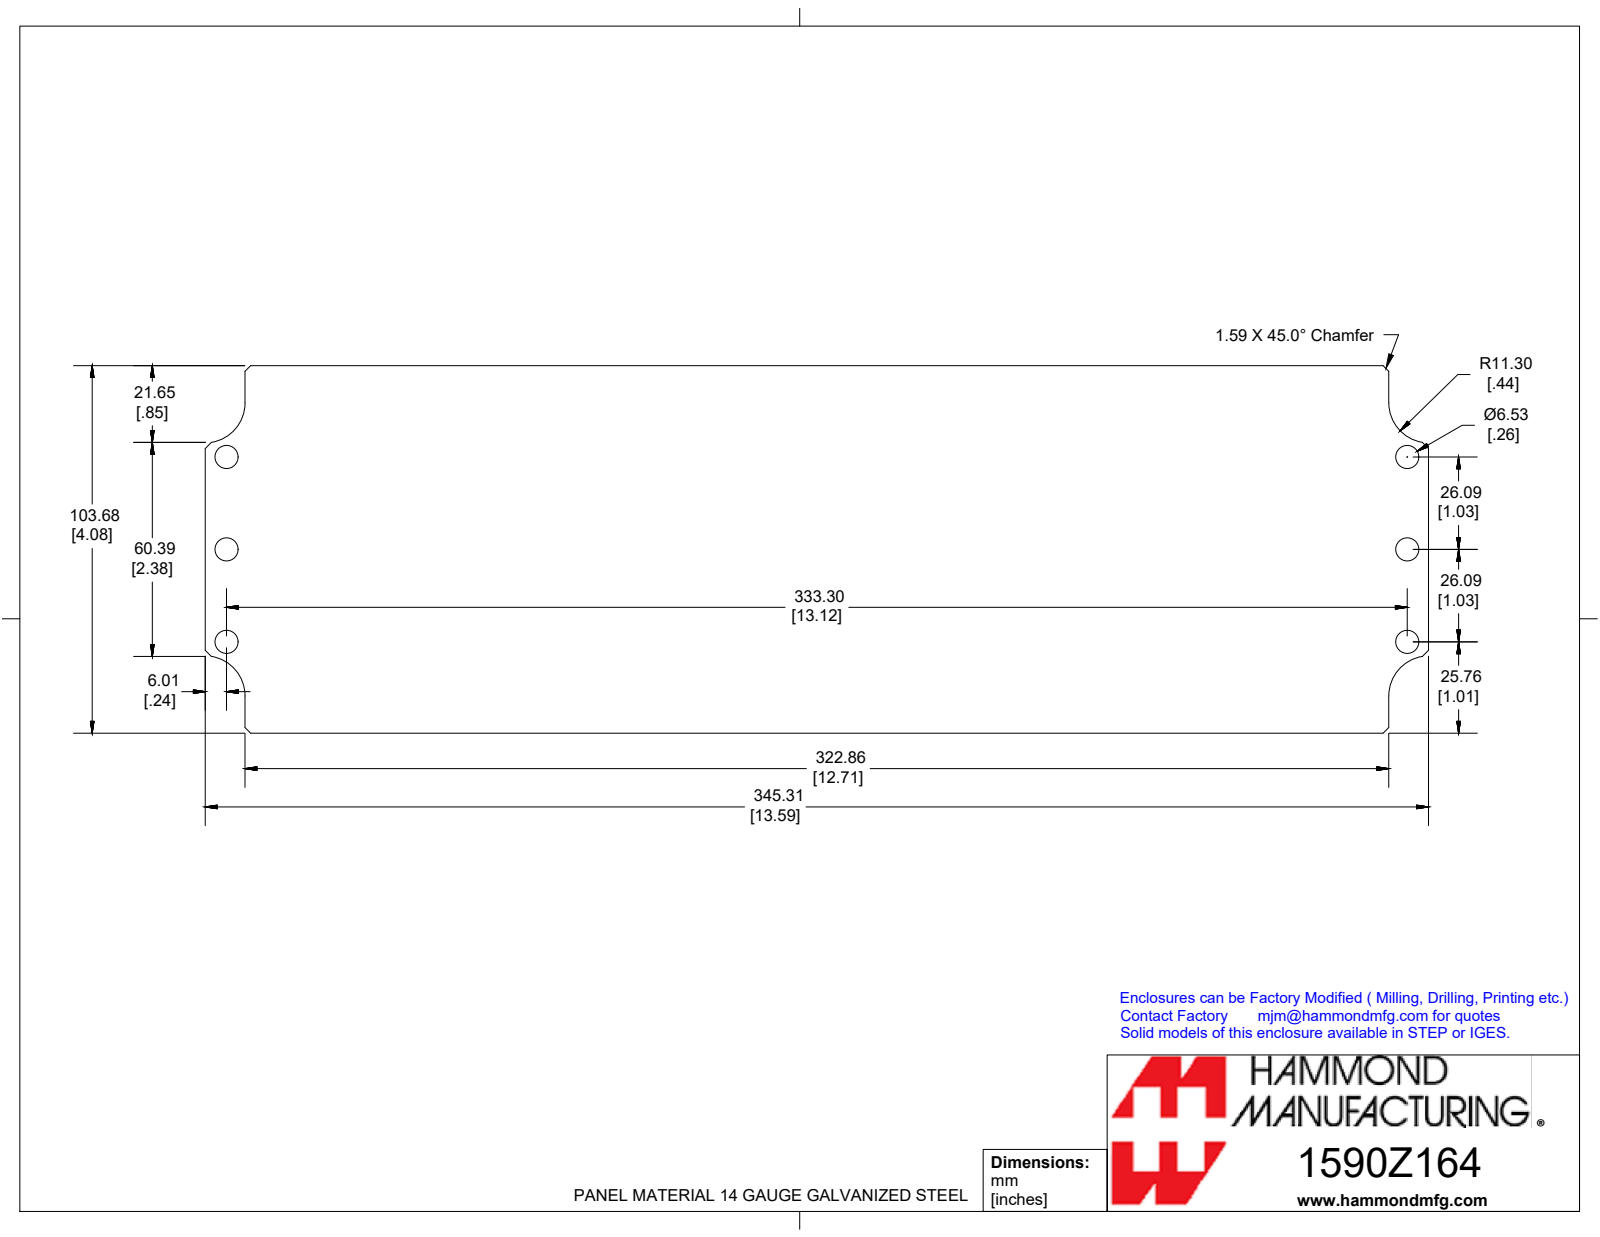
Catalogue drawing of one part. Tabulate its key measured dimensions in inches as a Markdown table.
| quantity | value |
| --- | --- |
| part name | 1590Z164PL |
| STEP written by | SolidWorks 2019 (CONFIG_CONTROL_DESIGN) |
| units | inches |
| bodies | 1 solid, 28 faces (18 planar, 10 cylindrical, 0 other) |
| overall size | 13.595 × 4.082 × 0.064 |
| volume | 3.418 in³ |
| surface area | 110.1 in² |
| round holes (diameter × count) | 0.257 × 6 |
| partial cylindrical surfaces (radius × count) | 0.445 × 4 |
| main face-to-face distances | 0.063, 4.082, 13.595, 0.442, 13.153, 12.711, 0.294, 11.49, 11.196, 11.784 |
| hole center spacings | 1.027, 13.162, 13.122, 2.054, 13.282 |
